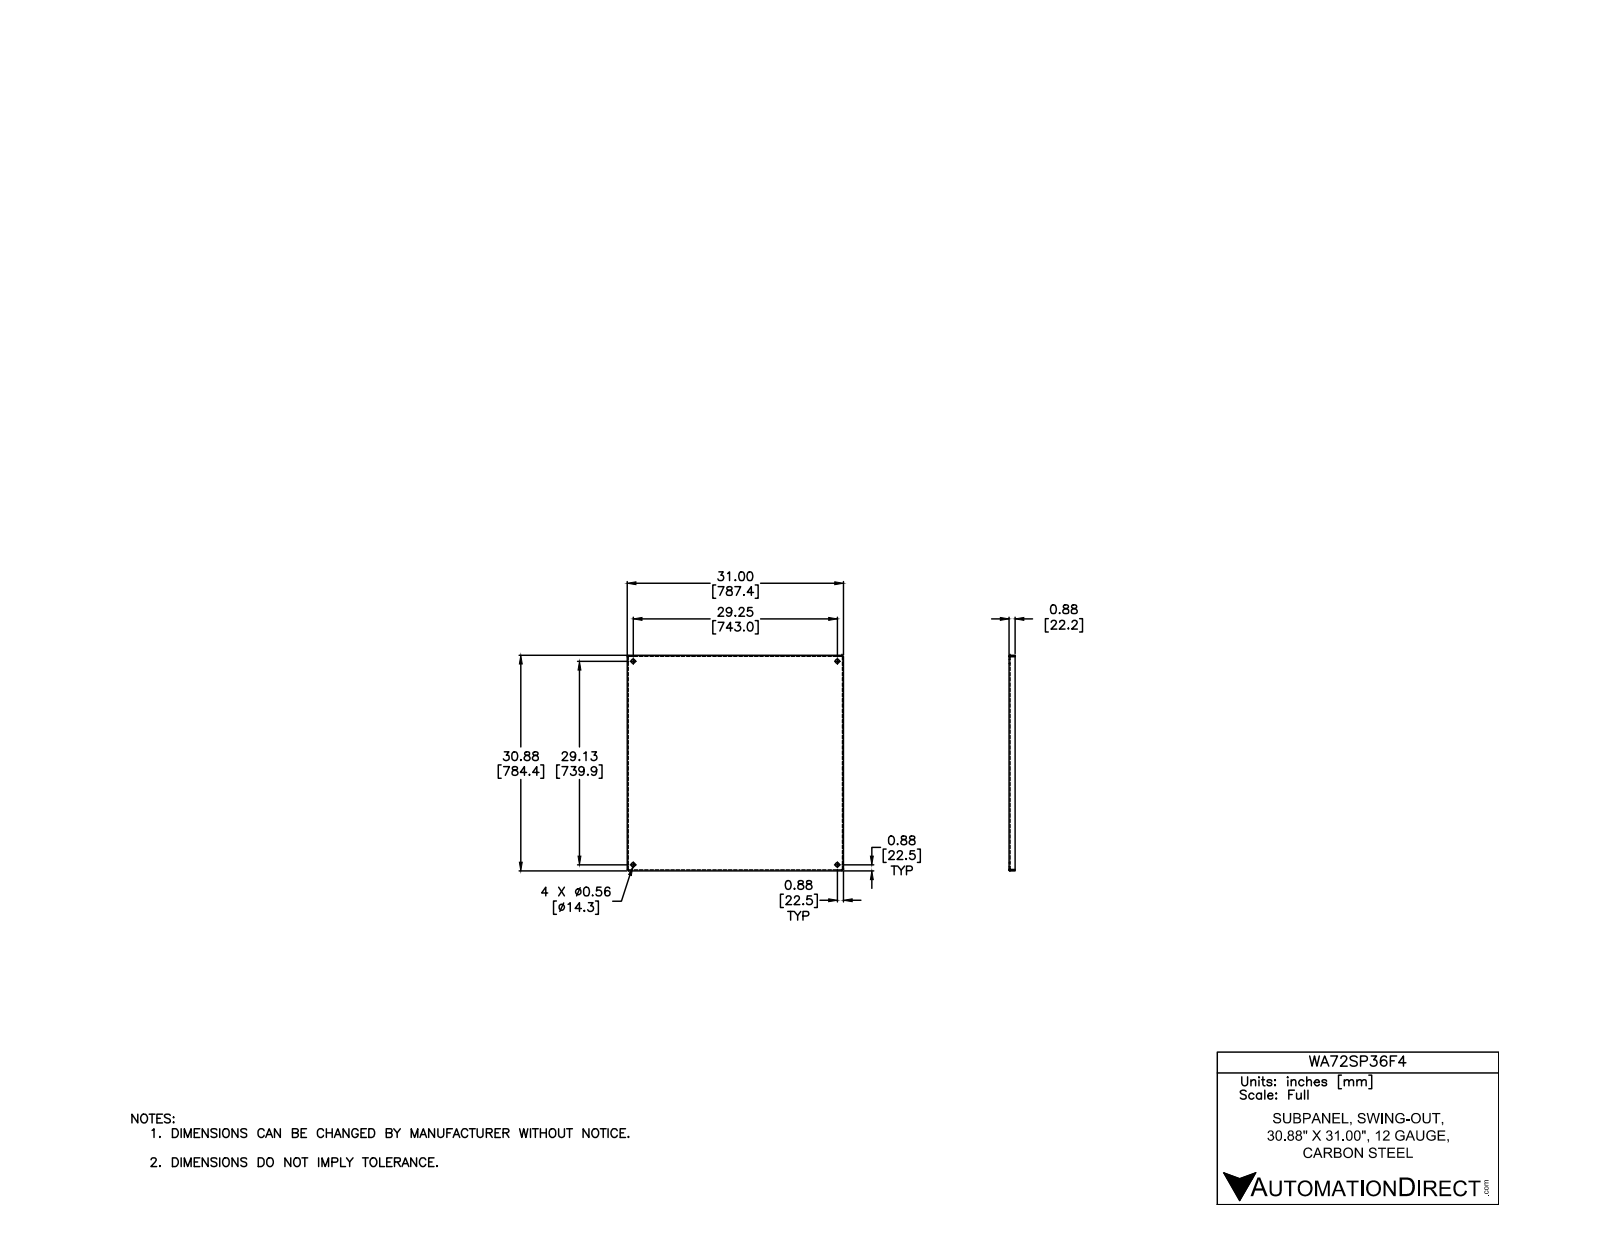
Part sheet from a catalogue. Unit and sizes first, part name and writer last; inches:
Units: inches
Overall size (bounding box): 31 × 30.88 × 0.875
Round holes (diameter × count): ⌀0.563 ×4
Partial cylindrical surfaces — rounded edges, fillets, slot ends (radius × count): R0.031 ×4, R0.125 ×4
Main face-to-face distances: 0.094, 30.786, 30.906, 30.693, 30.88, 31, 30.813, 0.781, 0.875, 0.16
Hole centre spacings: 29.13, 29.25, 41.281
Volume: 98.23 in³ · Surface area: 2 108 in²
Bodies: 1 solid, 42 faces (22 planar, 12 cylindrical, 8 other)
Part name (STEP PRODUCT): WA60SP24F3-WA90SP36F4
STEP written by: Autodesk Inventor 2012 (AUTOMOTIVE_DESIGN)
